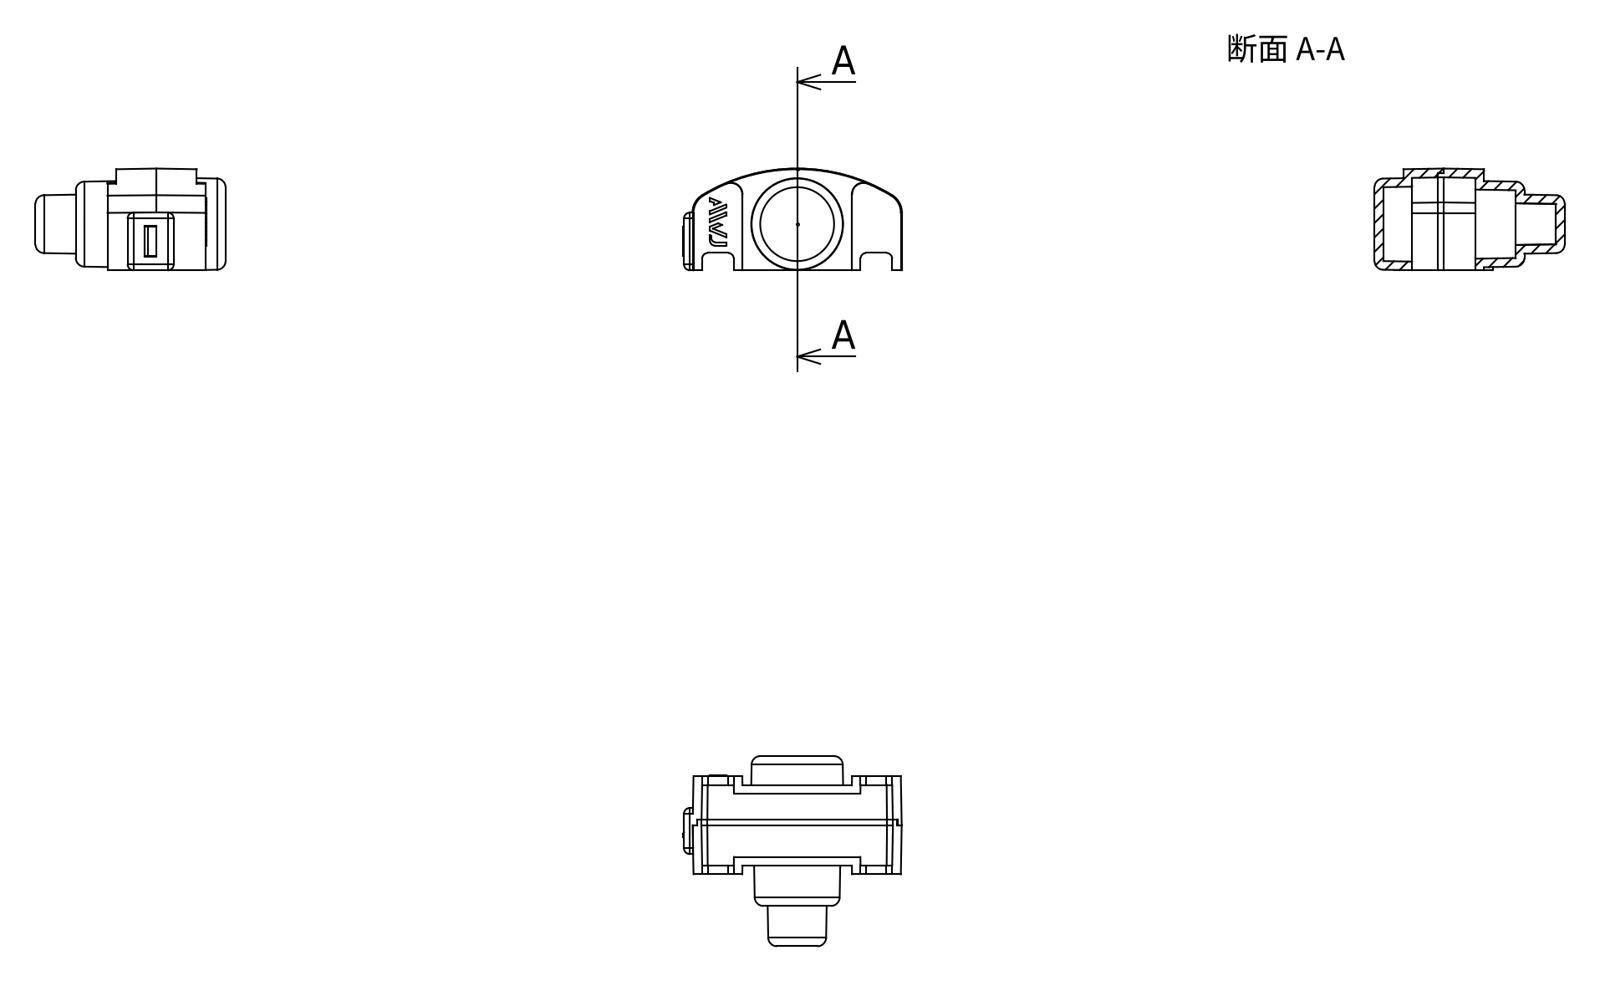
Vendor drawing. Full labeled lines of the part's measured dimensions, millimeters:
STEP written by: Spatial InterOp 3D (CONFIG_CONTROL_DESIGN)
Units: millimetres
Bodies: 3 solids, 194 faces (124 planar, 32 cylindrical, 38 other)
Overall size (bounding box): 39 × 33 × 17.65
Volume: 4 001 mm³ · Surface area: 5 852 mm²
Partial cylindrical surfaces — rounded edges, fillets, slot ends (radius × count): R1 ×12, R2.12 ×2, R2.87 ×2, R2.92 ×2, R0.4 ×1, R0.7 ×1, R0.77 ×1, R0.91 ×1
Main face-to-face distances: 1.5, 14, 12.5, 15.5, 3, 7, 5.5, 11, 8.5, 5
